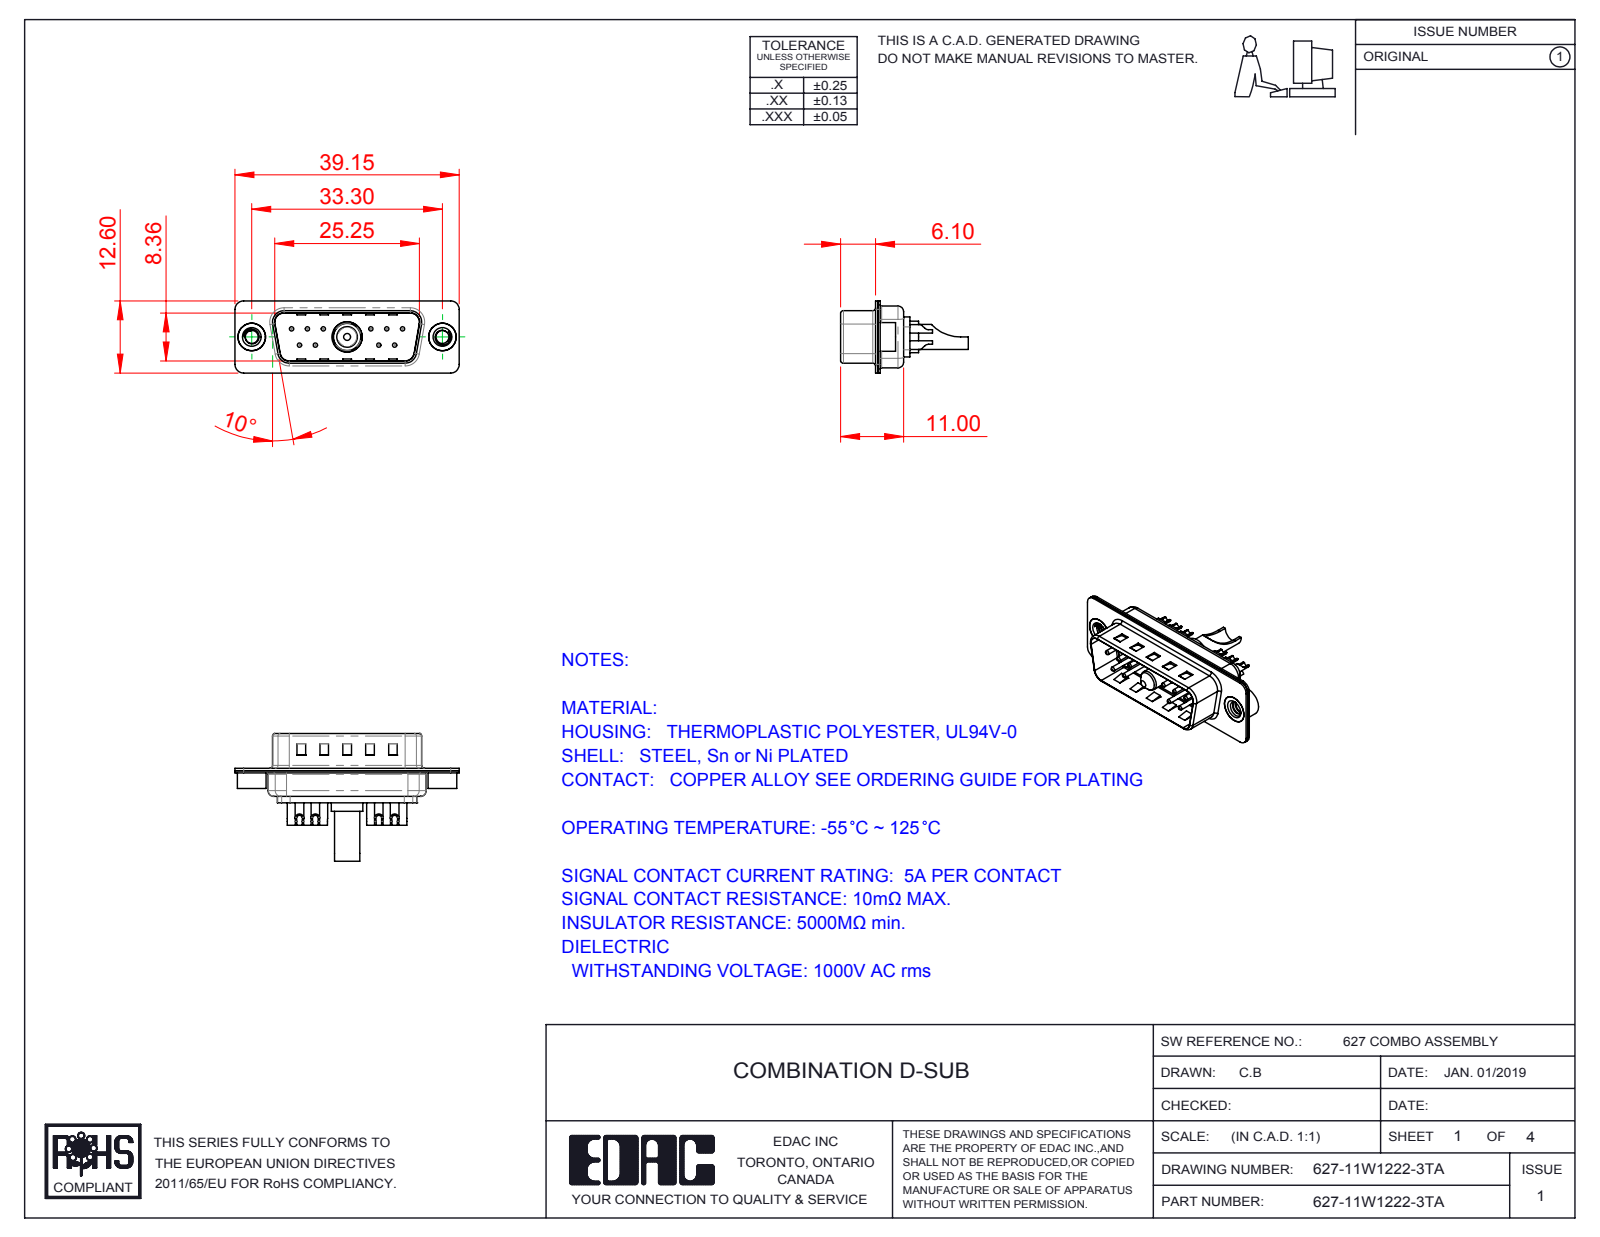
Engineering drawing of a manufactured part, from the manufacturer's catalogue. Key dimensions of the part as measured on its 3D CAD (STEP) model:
Part name (STEP PRODUCT): 627Combo Contact Row 2_22; 627Combo Shell Front_15 Contacts; 627Combo Shell Rear_15 Contacts; 627Combo Threaded Rivet_A (+5 more)
STEP written by: SolidWorks 2016 (CONFIG_CONTROL_DESIGN)
Units: millimetres
Bodies: 17 solids, 768 faces (251 planar, 320 cylindrical, 197 other)
Overall size (bounding box): 39.15 × 22.3 × 12.6
Volume: 1 952 mm³ · Surface area: 4 975 mm²
Round holes (diameter × count): ⌀0.75 ×10, ⌀1 ×10, ⌀1.6 ×10, ⌀2 ×10, ⌀2.26 ×2, ⌀4 ×2, ⌀4.8 ×2, ⌀3.5 ×1, ⌀4.85 ×1, ⌀5.3 ×1
Round bosses / shafts (diameter × count): ⌀1.5 ×10, ⌀5 ×2, ⌀4.9 ×2, ⌀5.5 ×1, ⌀5.2 ×1, ⌀4.75 ×1, ⌀4.4 ×1, ⌀3.75 ×1
Partial cylindrical surfaces — rounded edges, fillets, slot ends (radius × count): R1.5 ×20, R2 ×12, R1 ×9, R0.5 ×8, R1.6 ×8, R0.25 ×4, R0.6 ×4, R0.65 ×4
Main face-to-face distances: 0.4, 0.82, 9.58, 8.76, 0.8, 1.5, 1.4, 5.6, 5.2, 6
Hole centre spacings: 3.16, 2.77, 13.85, 11.08, 16.62, 5.03, 5.04, 5.54
